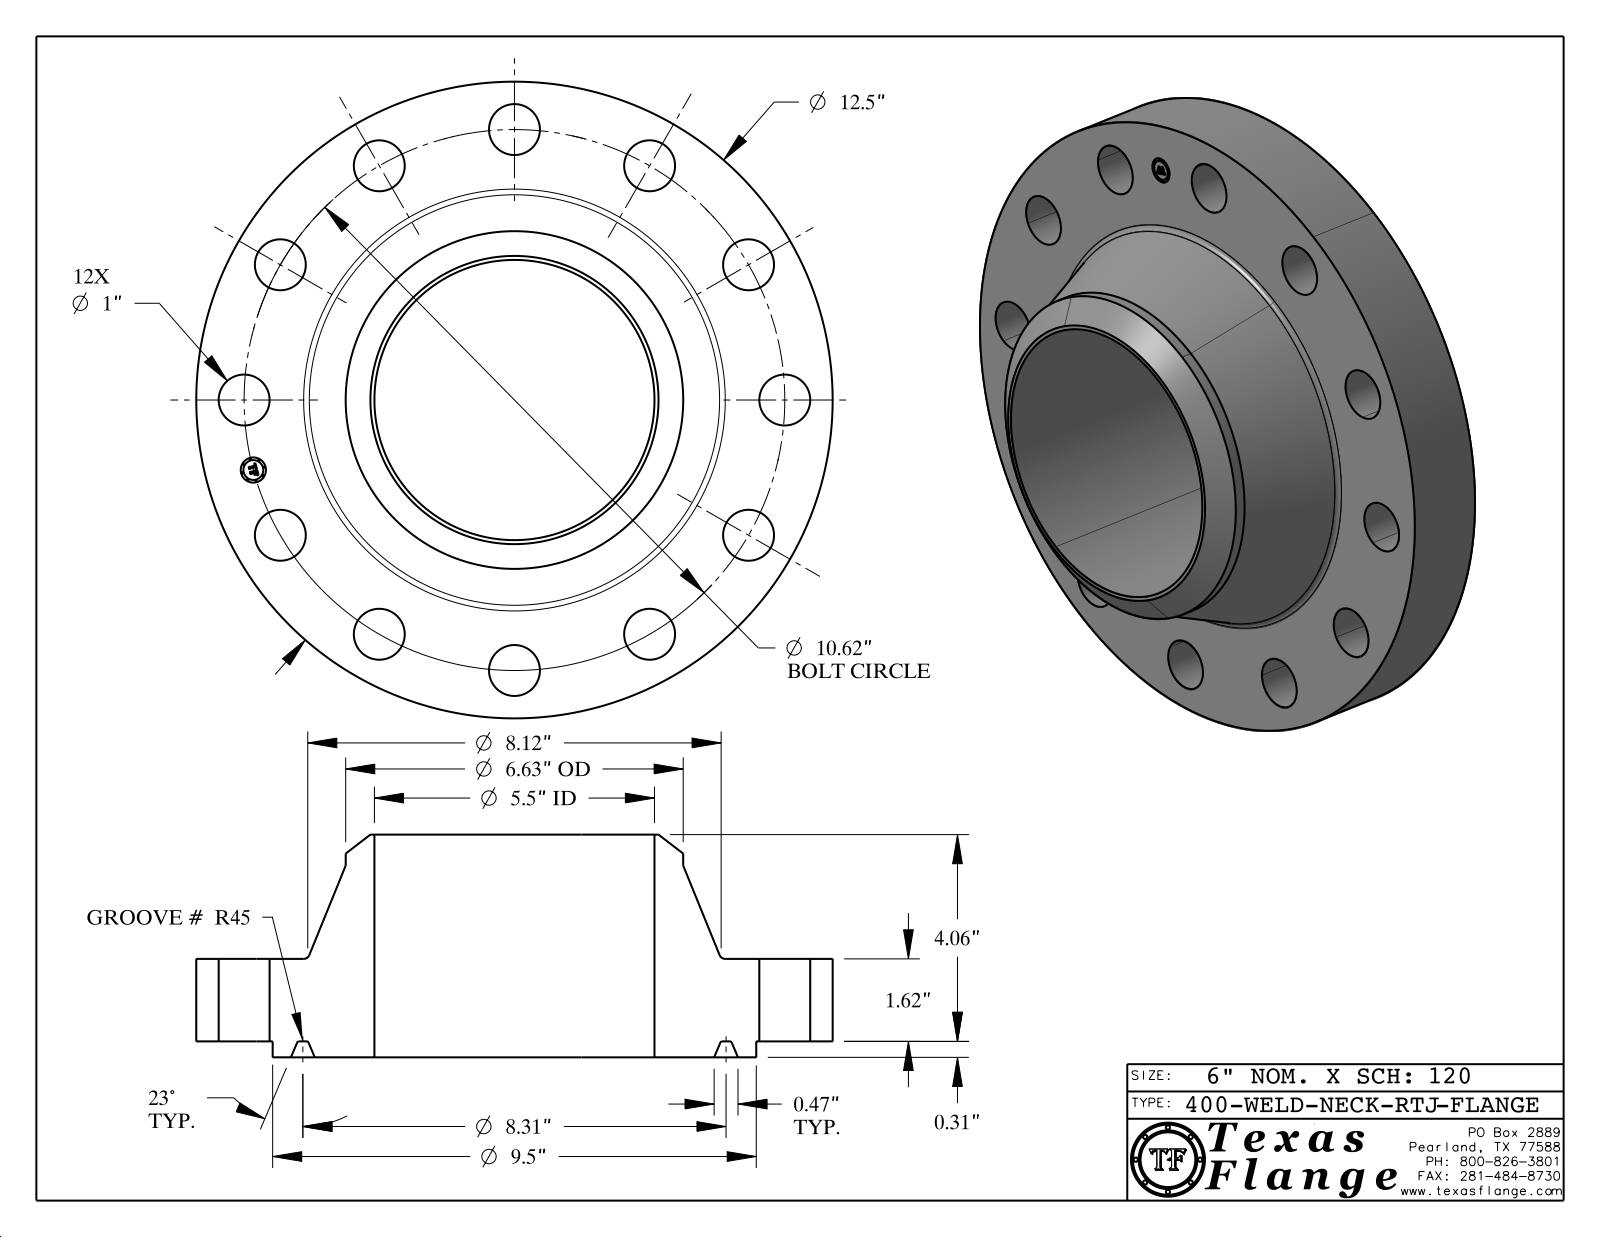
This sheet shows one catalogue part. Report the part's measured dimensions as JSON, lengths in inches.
{"part_name": "400-WELD-NECK-RTJ", "step_written_by": "CATIA V5 STEP AP214 (AUTOMOTIVE_DESIGN)", "units": "inches", "bodies": {"solids": 1, "faces": 437, "planar": 371, "cylindrical": 52, "other": 14}, "overall_size": [12.5, 12.5, 4.373], "volume_in3": 196.8, "surface_area_in2": 434.7, "round_holes": [[1, 12], [0.495, 1], [5.501, 1]], "round_bosses_or_shafts": [[0.03, 8], [12.5, 1], [9.5, 1], [6.63, 1], [0.39, 1]], "face_to_face_distances": [1.62, 0.313, 1.933, 4.373, 4.06, 2.44, 1.918, 1.605, 0.015, 2.455], "hole_center_spacings": [5.31, 10.258, 2.749, 7.509, 9.197, 10.62, 5.31, 2.748]}
